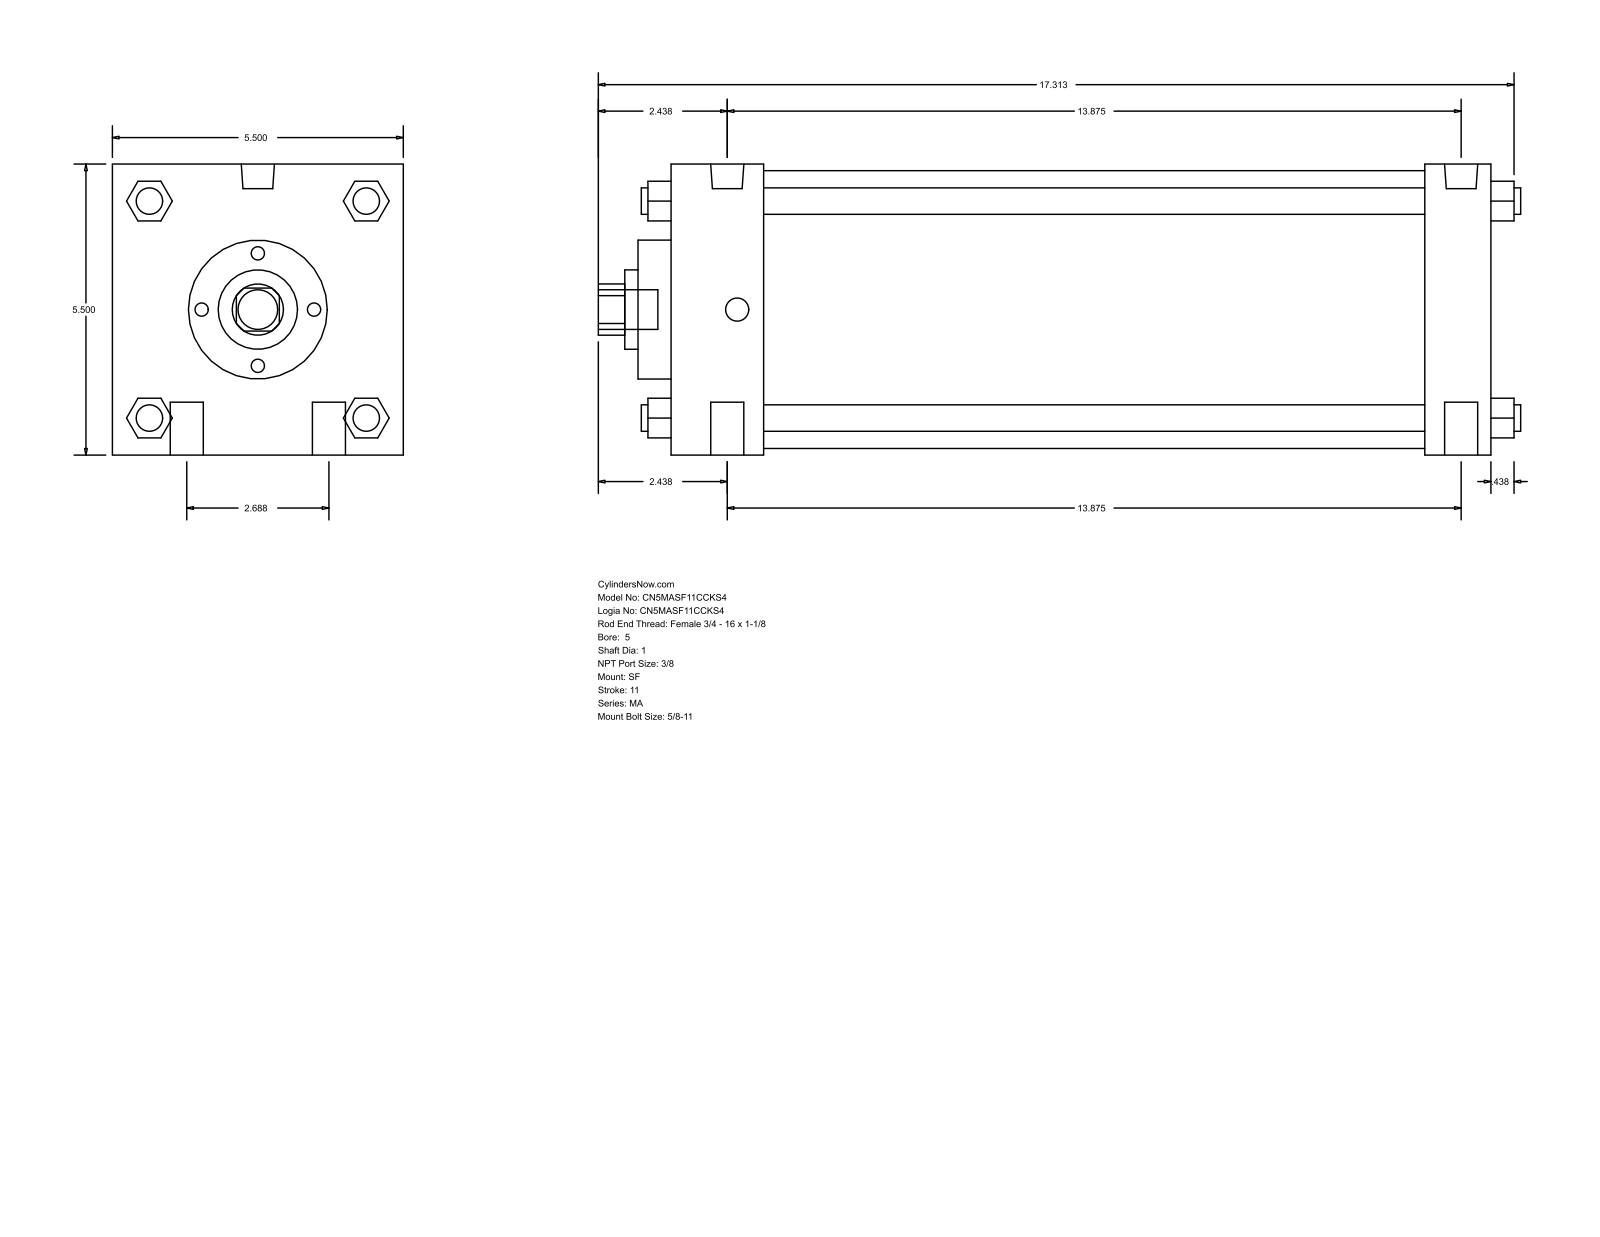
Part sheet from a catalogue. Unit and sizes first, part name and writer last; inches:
Units: inches
Overall size (bounding box): 17.437 × 5.5 × 5.5
Round holes (diameter × count): ⌀1 ×1, ⌀1.5 ×1, ⌀2.625 ×1, ⌀5.25 ×1
Round bosses / shafts (diameter × count): ⌀0.625 ×4, ⌀0.5 ×4, ⌀0.627 ×2, ⌀0.437 ×2, ⌀0.75 ×1
Partial cylindrical surfaces — rounded edges, fillets, slot ends (radius × count): R0.484 ×1
Main face-to-face distances: 5.5, 15.5, 1.75, 14.25, 12.5, 13.75, 1.25, 0.625, 2.375, 14.875
Bodies: 0 solids, 126 faces (95 planar, 31 cylindrical, 0 other)
Part name (STEP PRODUCT): MA_SF__0500_1
STEP written by: GSSL Pune (CONFIG_CONTROL_DESIGN)
